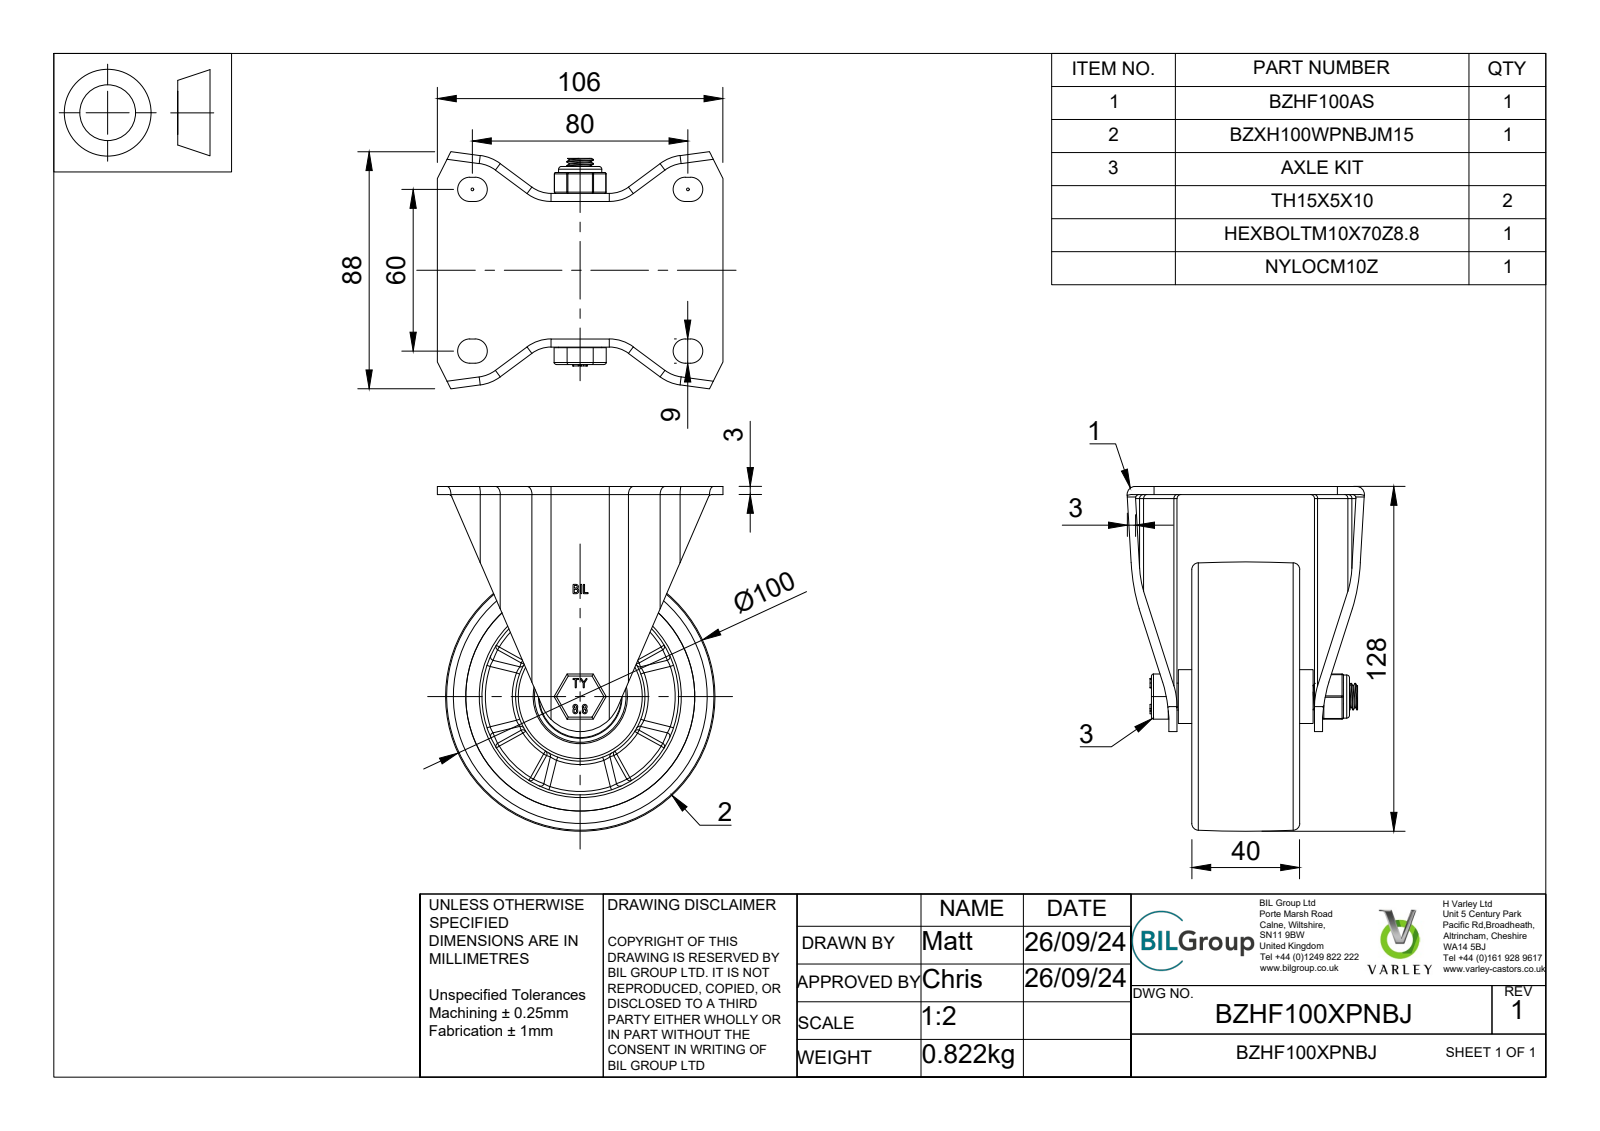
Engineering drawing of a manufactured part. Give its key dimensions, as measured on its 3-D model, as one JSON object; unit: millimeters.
{"part_name": "BZHF100XPNBJ v4; BZHF100AS v1; ZINC PLATED, PRESSED STEEL BRACKET; BZXH100WPNBJM15 v1 (+7 more)", "step_written_by": "Autodesk Translation Framework v13.20.0.188 (AUTOMOTIVE_DESIGN)", "units": "millimeters", "bodies": {"solids": 35, "faces": 1238, "planar": 422, "cylindrical": 217, "other": 599}, "overall_size": [128, 106, 88], "volume_mm3": 285423, "surface_area_mm2": 133065, "round_holes": [[10, 1], [10.25, 1], [10.5, 1], [12, 1], [15, 1], [22.5, 1], [30, 1], [31, 1], [32, 1], [35, 1], [73, 1], [85, 1]], "round_bosses_or_shafts": [[48, 1], [30.5, 1], [23, 1], [22, 1], [20, 1], [18, 1], [16, 1], [14.75, 1]], "partial_cylinders_radius": [[0.5, 18], [1.5, 12], [3, 10], [4.5, 8], [0.75, 6], [12, 5], [6, 4], [8, 4]], "face_to_face_distances": [3, 5.5, 45.5, 8.5, 48.5, 54, 40, 3.01, 25.27, 5]}
